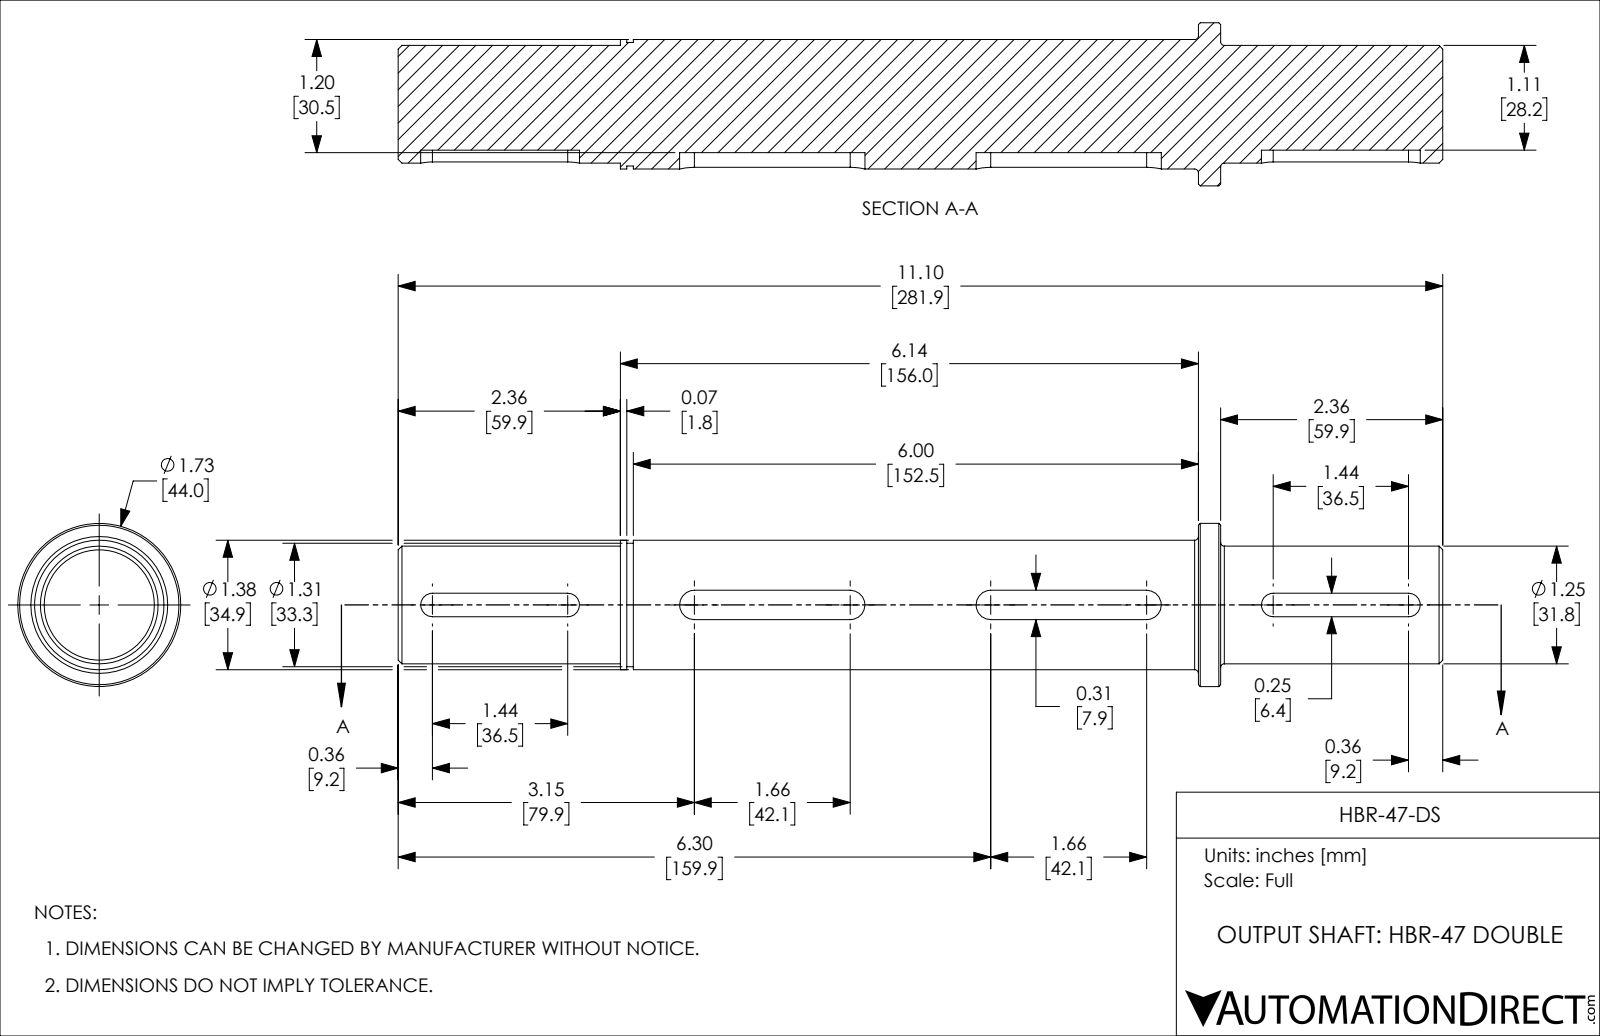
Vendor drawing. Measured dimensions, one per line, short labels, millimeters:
name: HBR-47-DS
written by: SolidWorks 2018 (AUTOMOTIVE_DESIGN)
unit: mm
bodies: 1 solid, 55 faces (19 planar, 24 cylindrical, 12 other)
size: 281.9 × 44 × 44
volume: 248 100 mm³; area: 34 280 mm²
bosses: 1× ⌀44, 1× ⌀34.9, 1× ⌀33.3, 1× ⌀31.8
rounds: 4× R3.2, 4× R4
face distances: 59.9, 221.9, 281.9, 0.7, 216, 6, 65.9, 0.8, 7.1, 8
